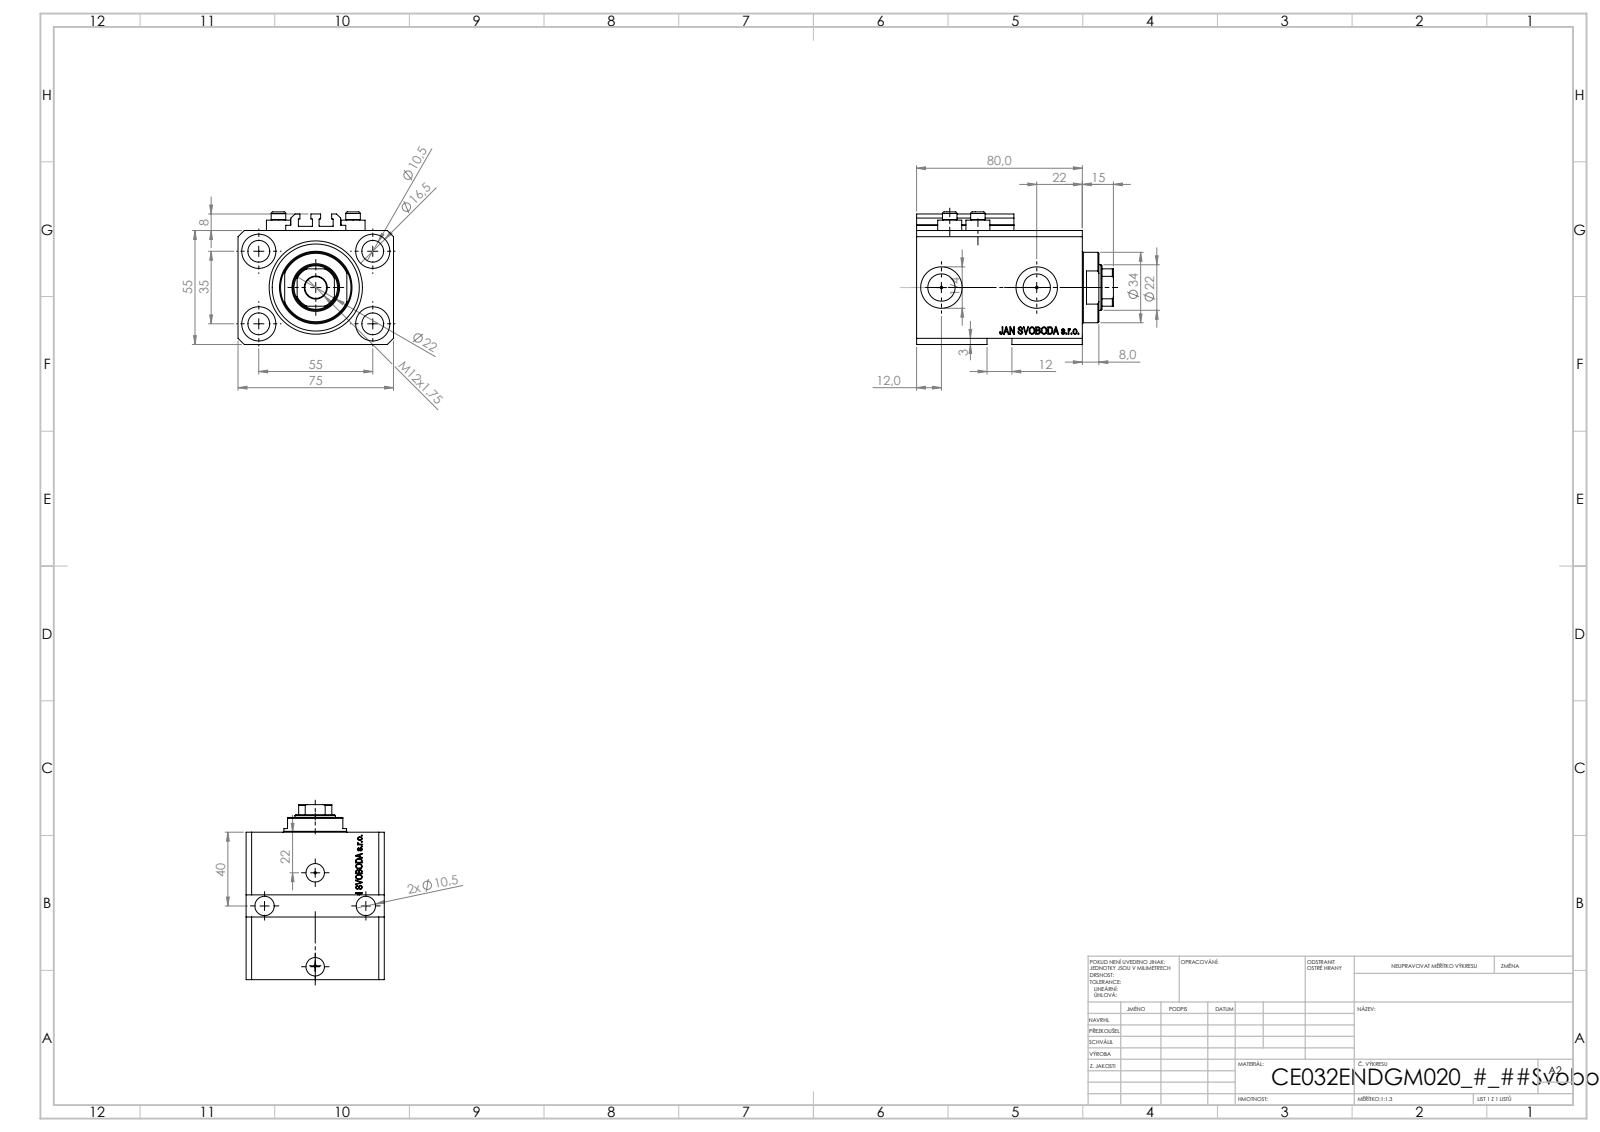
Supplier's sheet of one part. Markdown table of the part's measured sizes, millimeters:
| quantity | value |
| --- | --- |
| part name | V250CE_E_Body; ALLEN BOLT V250CE; V250CE_VC_E; V250CE_C_VCP |
| STEP written by | SolidWorks 2019 (CONFIG_CONTROL_DESIGN) |
| units | millimeters |
| bodies | 8 solids, 1080 faces (518 planar, 138 cylindrical, 424 other) |
| overall size | 95 × 75 × 64 |
| volume | 280 274 mm³ |
| surface area | 75 612 mm² |
| round holes (diameter × count) | 10.5 × 7, 1.25 × 4, 4 × 4, 16.5 × 4, 10 × 2, 13.16 × 2, 20 × 2, 22 × 1, 32 × 1, 45 × 1 |
| round bosses / shafts (diameter × count) | 11.6 × 4, 7 × 4, 34 × 1 |
| partial cylindrical surfaces (radius × count) | 0.2 × 10, 10.5 × 1 |
| main face-to-face distances | 55, 75, 15, 80, 65, 3, 9.9, 55.1, 70.1, 54 |
| hole center spacings | 32.6, 55, 13.6, 14.09, 19.89, 20.12, 25.81, 28.48 |
